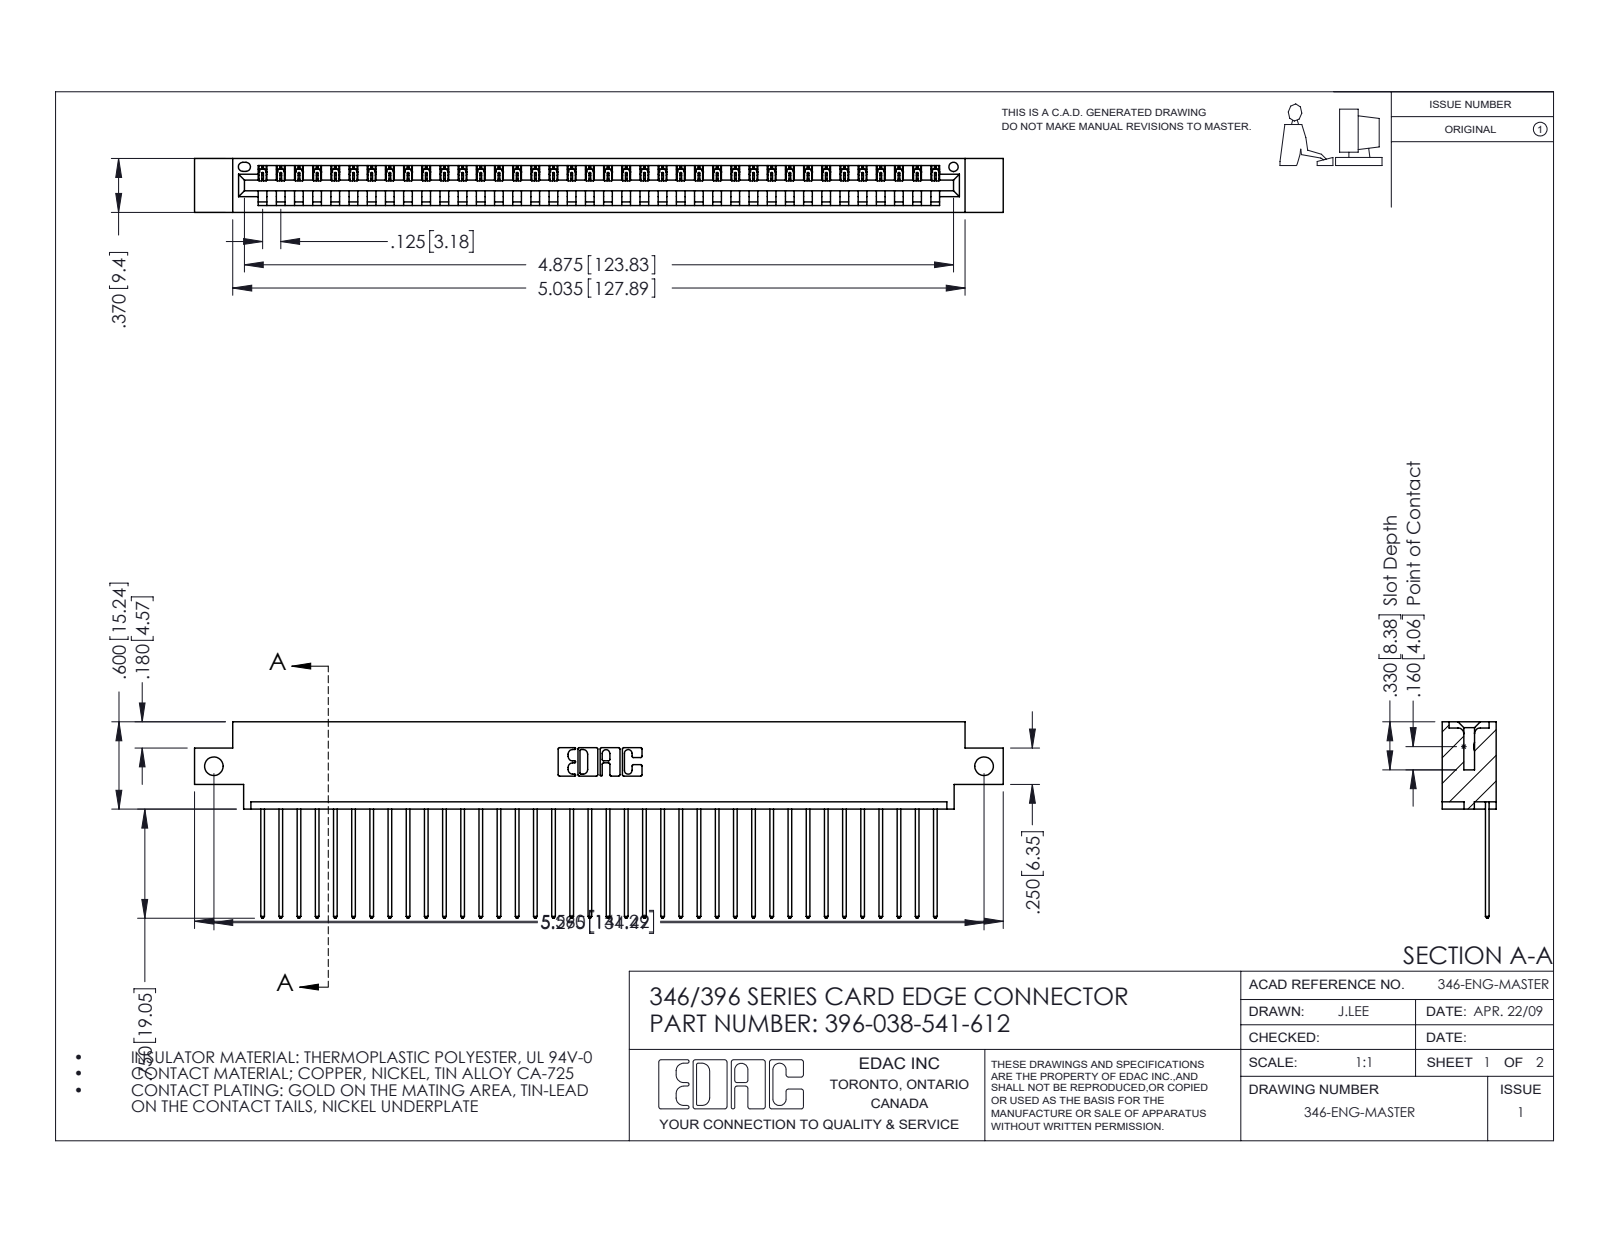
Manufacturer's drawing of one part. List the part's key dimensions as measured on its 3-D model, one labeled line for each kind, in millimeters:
Part name (STEP PRODUCT): 396-038-541-612; 345-292-001_345-293-141; 346 Part_0.170 Offset - Side Mount
STEP written by: SolidWorks 2016 (CONFIG_CONTROL_DESIGN)
Units: millimetres
Bodies: 39 solids, 2330 faces (1600 planar, 730 cylindrical, 0 other)
Overall size (bounding box): 141.2 × 34.3 × 9.4
Volume: 13 400 mm³ · Surface area: 17 440 mm²
Round holes (diameter × count): ⌀3.3 ×2, ⌀1.6 ×1
Partial cylindrical surfaces — rounded edges, fillets, slot ends (radius × count): R0.2 ×76, R0.3 ×76, R0.3 ×22, R0.2 ×6, R0.8 ×6, R0.7 ×3, R0.8 ×2, R1 ×2
Main face-to-face distances: 1.2, 8.2, 9.4, 6.4, 1.8, 7.6, 0.6, 3.8, 5.6, 2.5
Hole centre spacings: 134.5
